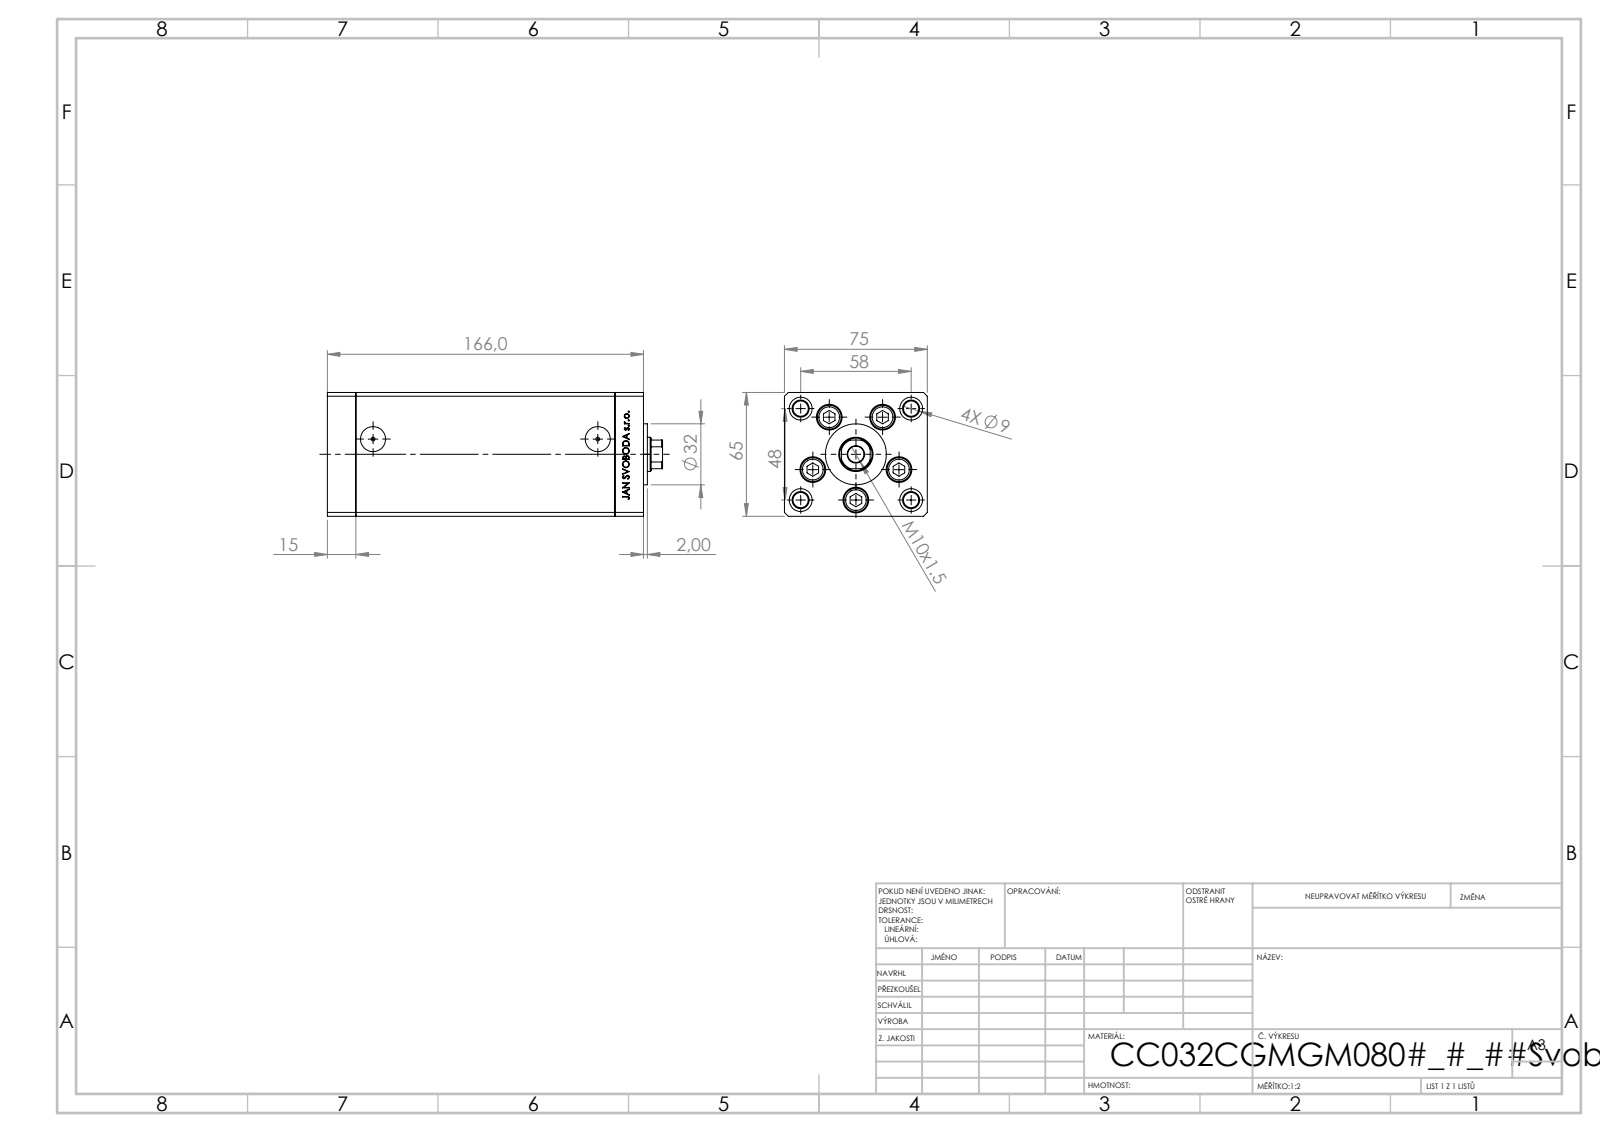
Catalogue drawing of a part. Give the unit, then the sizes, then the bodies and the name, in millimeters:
Units: millimetres
Overall size (bounding box): 176 × 75 × 65
Round holes (diameter × count): ⌀9 ×9, ⌀13.5 ×5, ⌀8 ×4, ⌀12 ×4, ⌀2 ×2, ⌀13.16 ×2, ⌀8.5 ×1, ⌀12.5 ×1, ⌀18 ×1
Round bosses / shafts (diameter × count): ⌀8 ×5, ⌀12.5 ×4, ⌀32 ×1
Partial cylindrical surfaces — rounded edges, fillets, slot ends (radius × count): R0.93 ×2, R8.5 ×1
Main face-to-face distances: 75, 65, 15, 136, 151, 166, 28, 142, 13, 9
Hole centre spacings: 24, 37.64, 15.67, 17.22, 27.71, 28.83, 29, 32.63
Volume: 680 499 mm³ · Surface area: 142 517 mm²
Bodies: 13 solids, 1169 faces (540 planar, 167 cylindrical, 462 other)
Part name (STEP PRODUCT): V220C_VC_C; V220C_C MIDDLE; ALLEN BOLT; V220C FRONT (+1 more)
STEP written by: SolidWorks 2019 (CONFIG_CONTROL_DESIGN)
